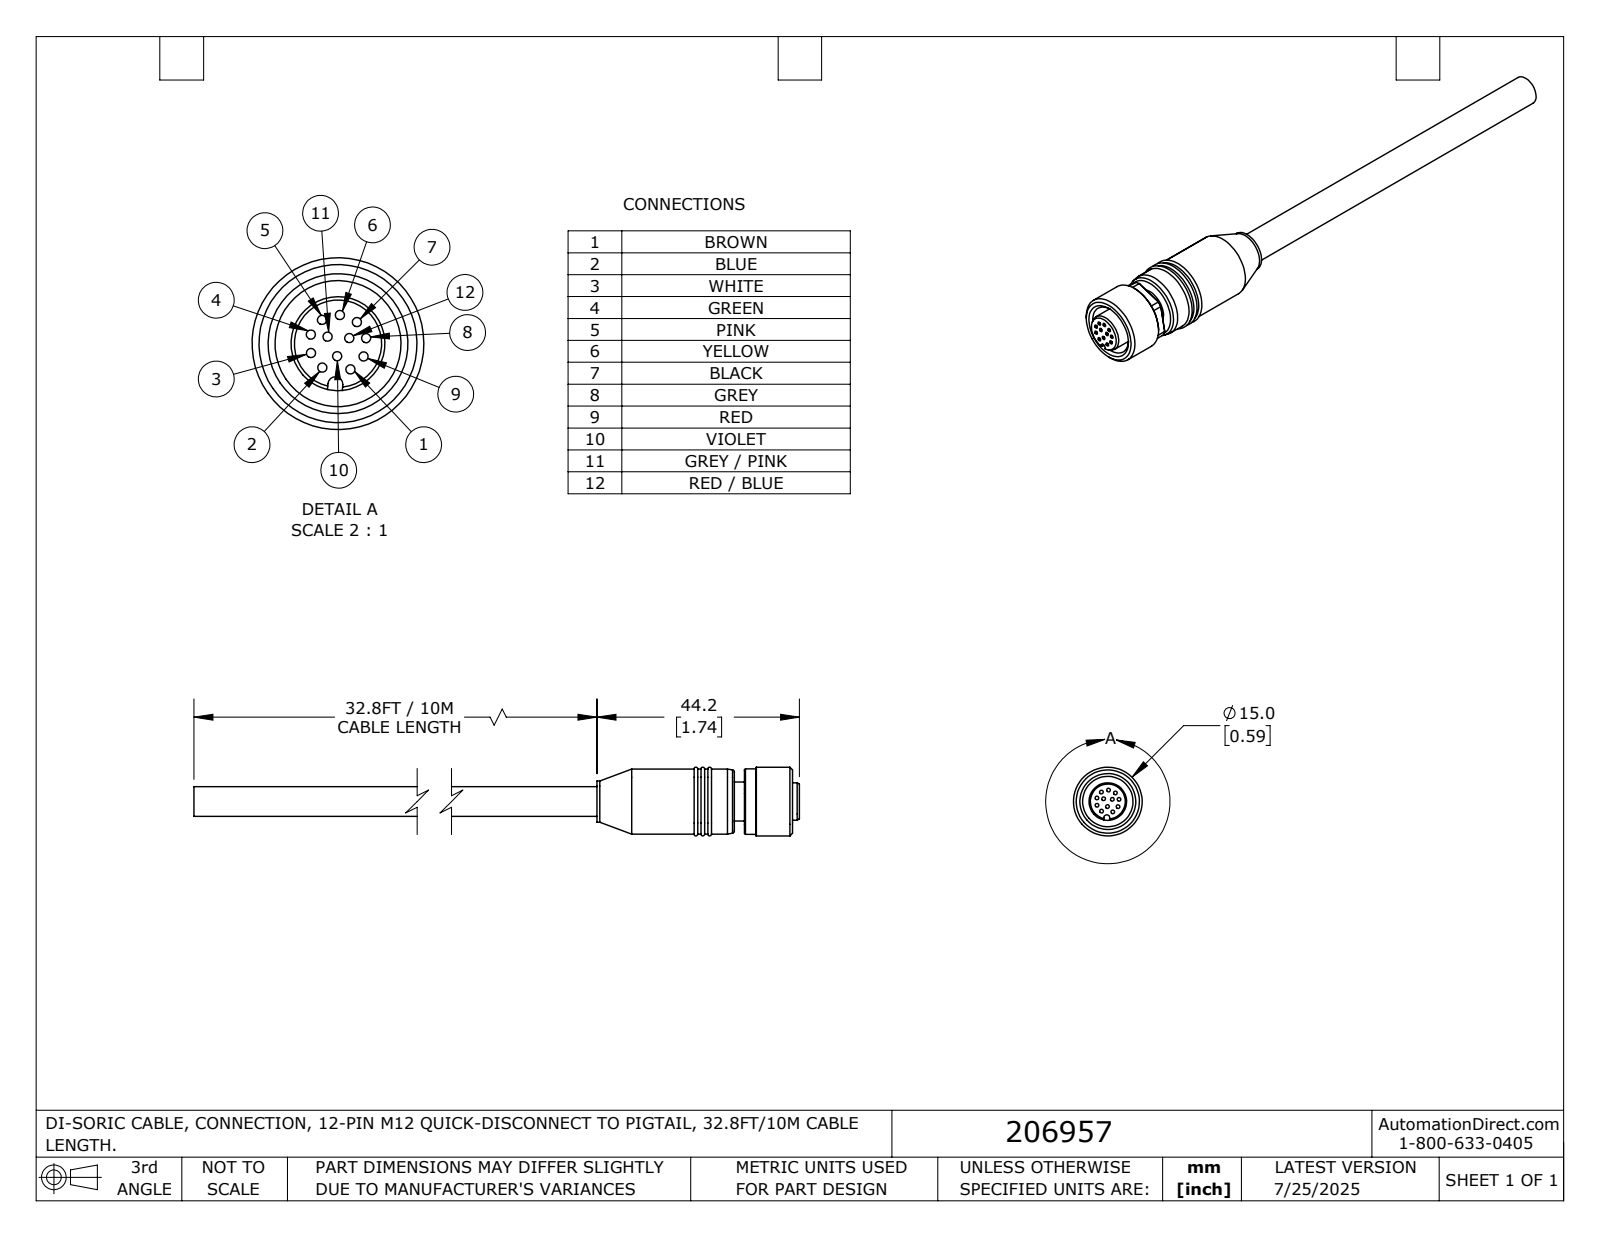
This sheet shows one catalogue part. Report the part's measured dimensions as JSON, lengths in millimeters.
{"part_name": "VKHM-Z-5_12-A", "step_written_by": "SolidWorks 2024 (AUTOMOTIVE_DESIGN)", "units": "millimeters", "bodies": {"solids": 1, "faces": 80, "planar": 35, "cylindrical": 29, "other": 16}, "overall_size": [130.2, 15, 15], "volume_mm3": 8809, "surface_area_mm2": 4776, "round_holes": [[0.8, 12], [11, 1]], "round_bosses_or_shafts": [[15, 1], [14.2, 1], [9, 1], [8.5, 1], [8.2, 1], [6.5, 1]], "partial_cylinders_radius": [[0.65, 1], [7.2, 1]], "face_to_face_distances": [2.2, 5.2, 3, 14.2, 12, 9, 116, 118.2, 121.2, 130.2], "hole_center_spacings": [1.61, 2.5, 3.05, 4.83, 1.1, 1.91, 3.6, 4.16]}
